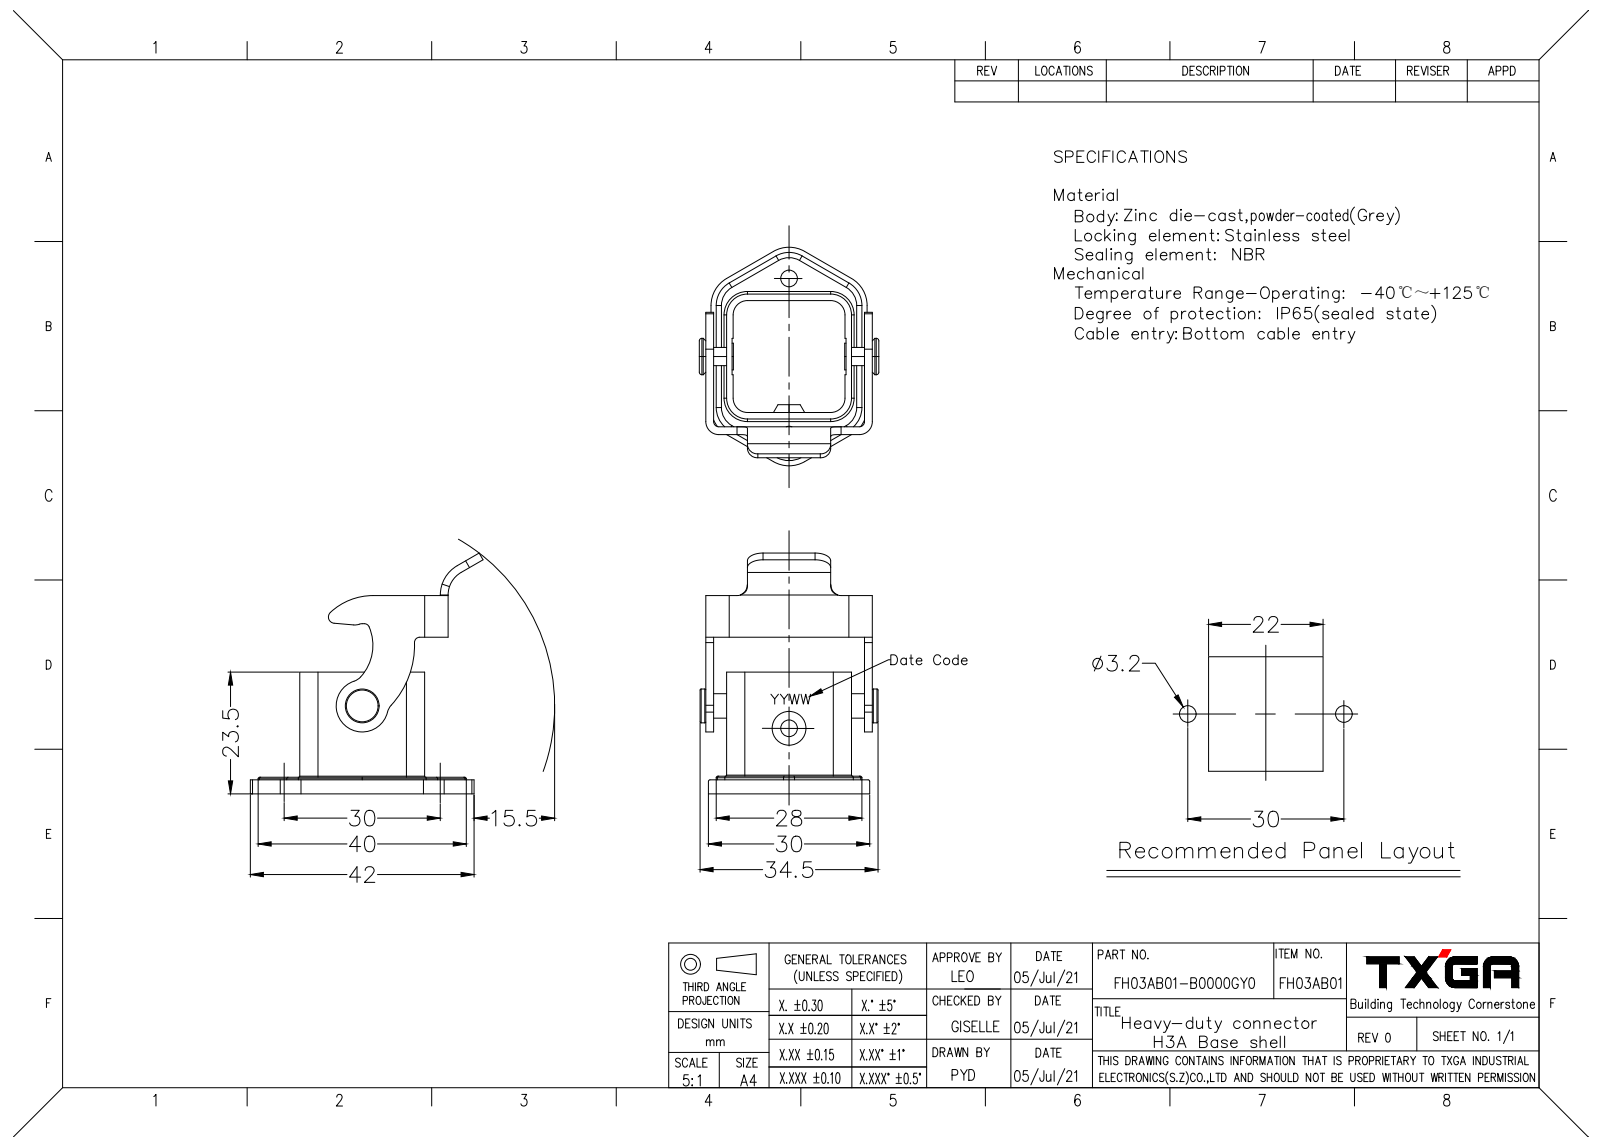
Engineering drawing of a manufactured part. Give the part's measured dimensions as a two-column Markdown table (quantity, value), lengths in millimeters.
| quantity | value |
| --- | --- |
| part name | FH03AB01-B0000GY0 H3A-BK-1L-REF（渲染） |
| STEP written by | SolidWorks 2021 (CONFIG_CONTROL_DESIGN) |
| units | millimeters |
| bodies | 1 solid, 178 faces (67 planar, 86 cylindrical, 25 other) |
| overall size | 44.75 × 42 × 34.5 |
| volume | 5 433 mm³ |
| surface area | 7 841 mm² |
| round holes (diameter × count) | 3.2 × 2, 2.09 × 1, 3 × 1, 6 × 1 |
| round bosses / shafts (diameter × count) | 7 × 1, 5.13 × 1, 3.5 × 1 |
| partial cylindrical surfaces (radius × count) | 1 × 9, 5 × 7, 2 × 6, 6 × 6, 4 × 5, 0.5 × 4, 2.75 × 4, 3 × 4 |
| main face-to-face distances | 1.25, 1.5, 22.75, 24, 28, 4, 2.5, 26.5, 30.5, 3 |
| hole center spacings | 30 |
